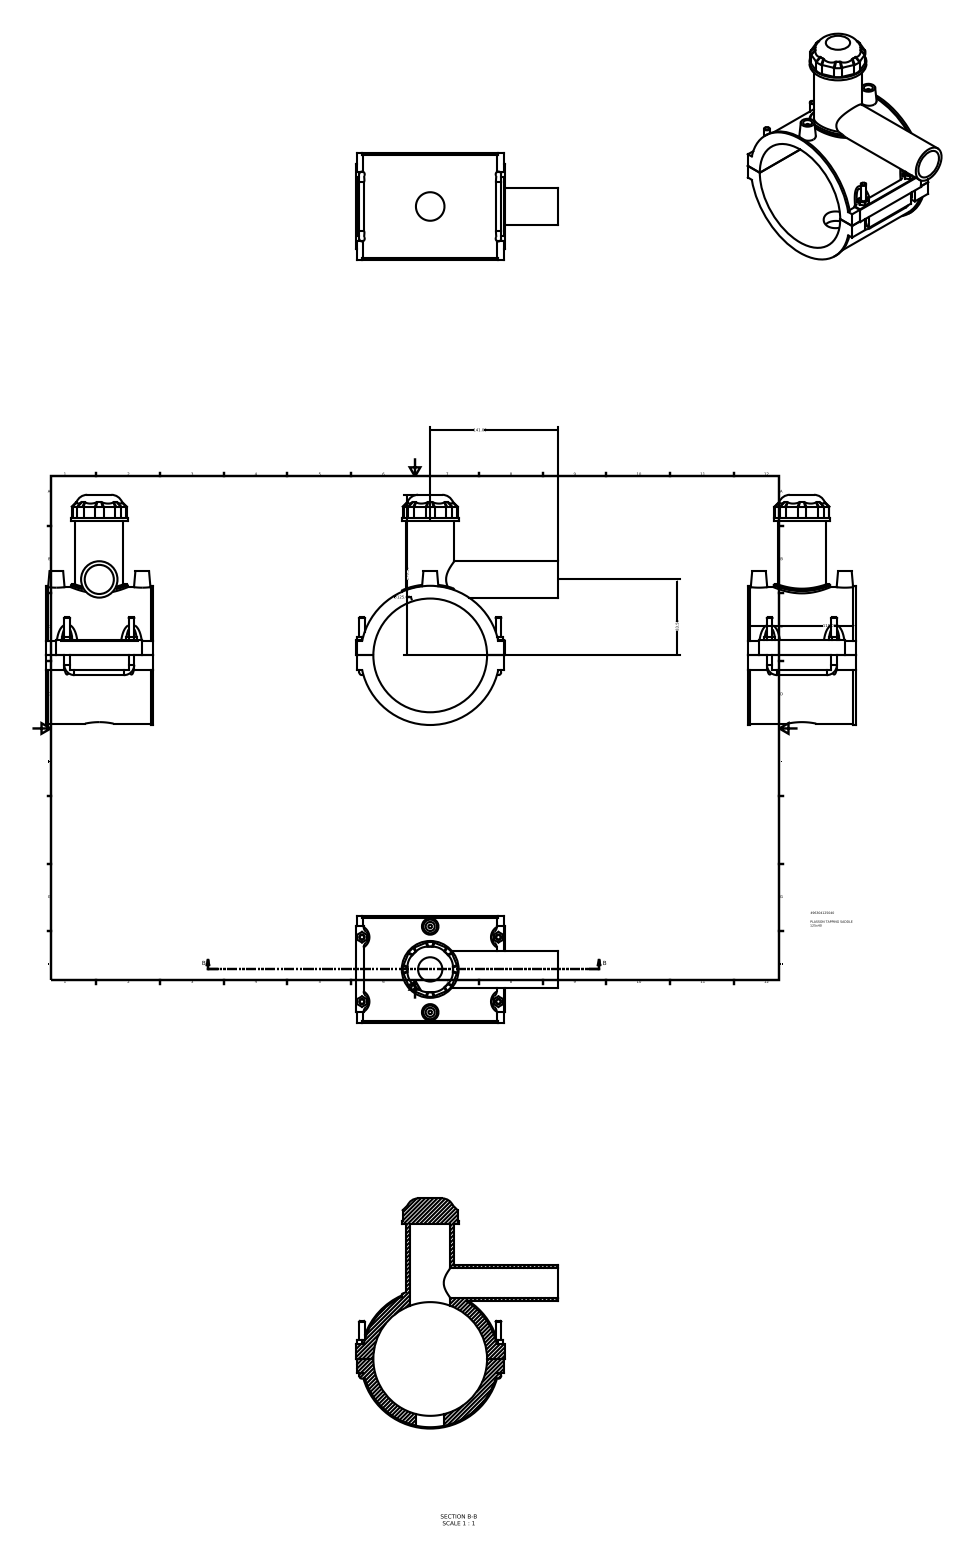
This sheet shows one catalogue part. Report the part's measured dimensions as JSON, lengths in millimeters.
{"part_name": "496304125040", "step_written_by": "Autodesk Inventor 2015 (AUTOMOTIVE_DESIGN)", "units": "millimeters", "bodies": {"solids": 1, "faces": 224, "planar": 125, "cylindrical": 55, "other": 44}, "overall_size": [253, 223, 118], "volume_mm3": 844563, "surface_area_mm2": 191492, "round_holes": [[10, 2], [31.36, 1], [32, 1], [43.75, 1], [125, 1]], "round_bosses_or_shafts": [[6, 4], [4, 2], [153, 1], [150, 1], [62.5, 1], [53.12, 1], [40, 1]], "partial_cylinders_radius": [[12.5, 8], [3, 6], [7.5, 4], [0.5, 1], [78, 1]], "face_to_face_distances": [118, 1, 163, 148.05, 147.95, 162, 15.57, 15.67, 163.62, 32.25], "hole_center_spacings": [47.2, 94.4]}
